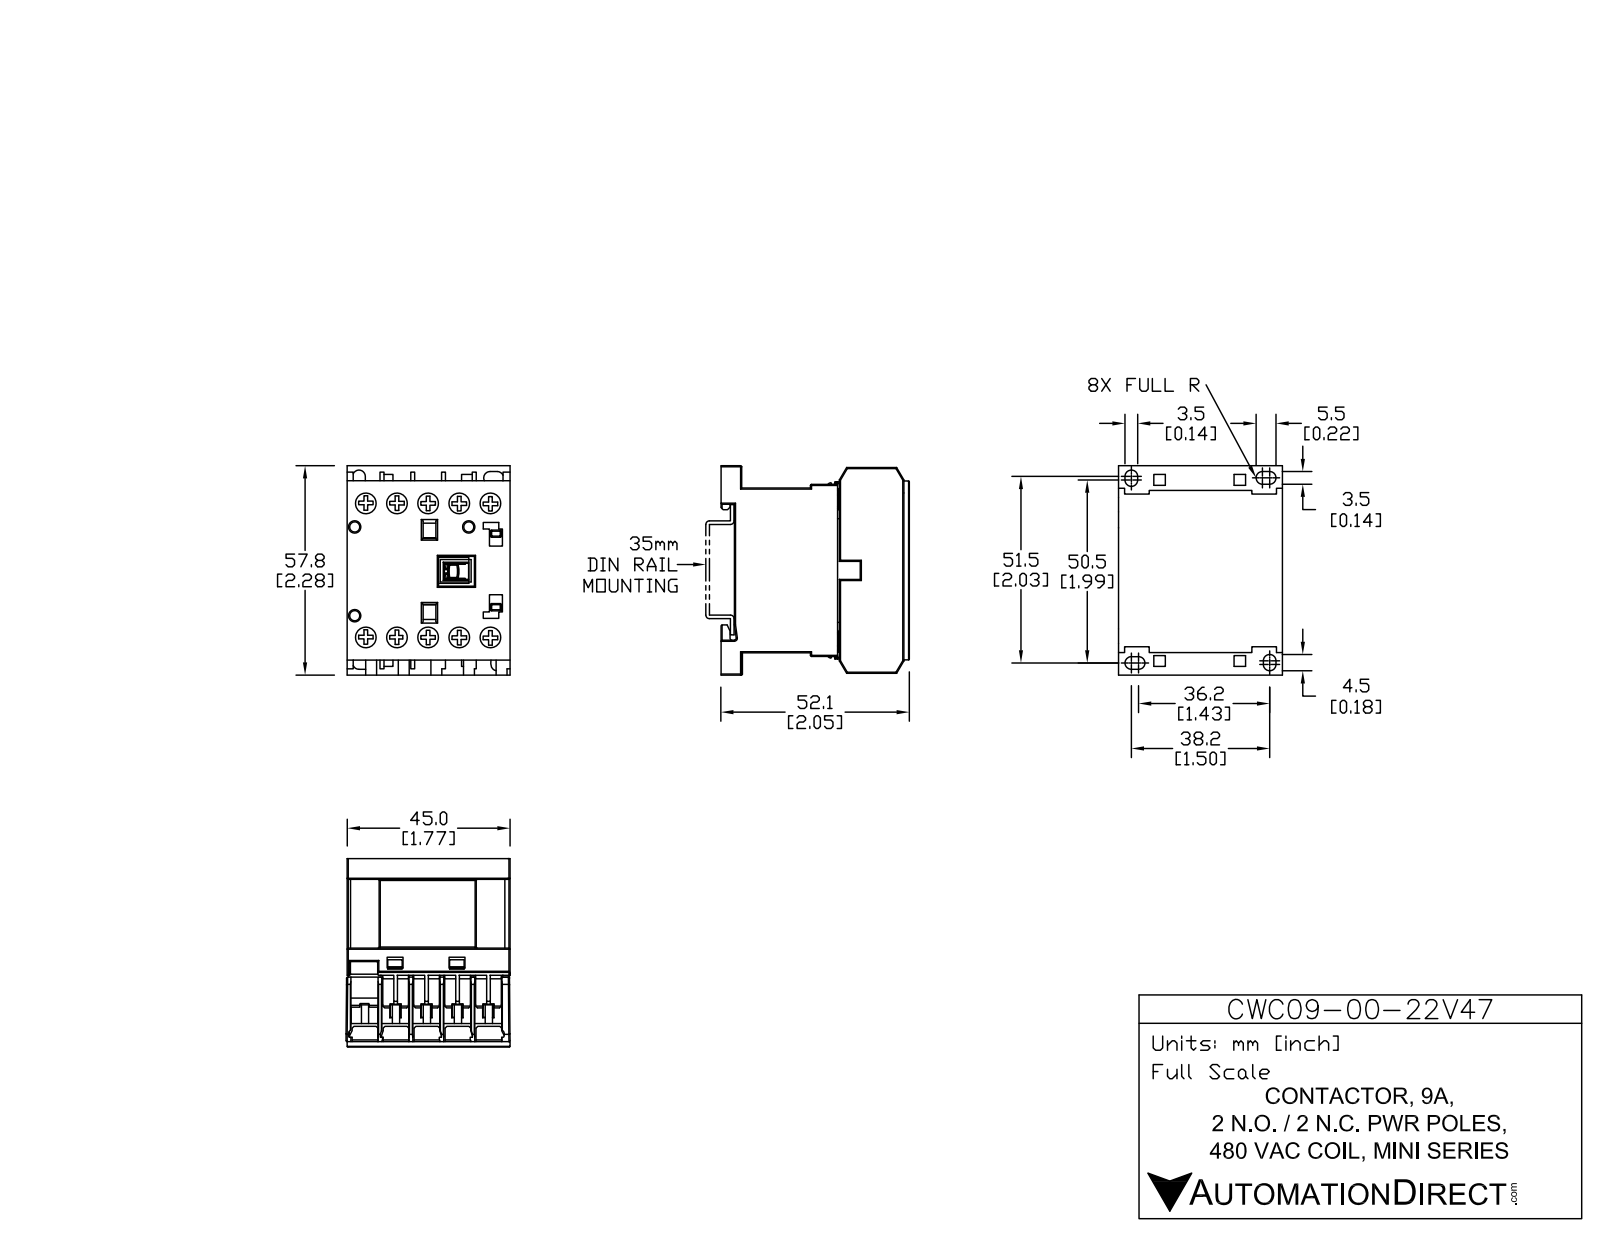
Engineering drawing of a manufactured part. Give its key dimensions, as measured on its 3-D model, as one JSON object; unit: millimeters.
{"part_name": "CWC09-00-22V47", "step_written_by": "SolidWorks 2013 (AUTOMOTIVE_DESIGN)", "units": "millimeters", "bodies": {"solids": 15, "faces": 535, "planar": 445, "cylindrical": 90, "other": 0}, "overall_size": [58.04, 52.12, 45.75], "volume_mm3": 97133, "surface_area_mm2": 30437, "round_holes": [[6.2, 10], [2.8, 3]], "round_bosses_or_shafts": [[5.9, 10]], "partial_cylinders_radius": [[0.3, 20], [1.72, 6], [1.73, 2], [0.32, 1], [0.42, 1], [0.55, 1]], "face_to_face_distances": [8.25, 45.5, 1.25, 16.5, 9.5, 5.5, 17.75, 5.13, 10.63, 7], "hole_center_spacings": [8.55, 37.94, 17.1, 40.72, 36.96, 25.65, 44.99, 6.91]}
